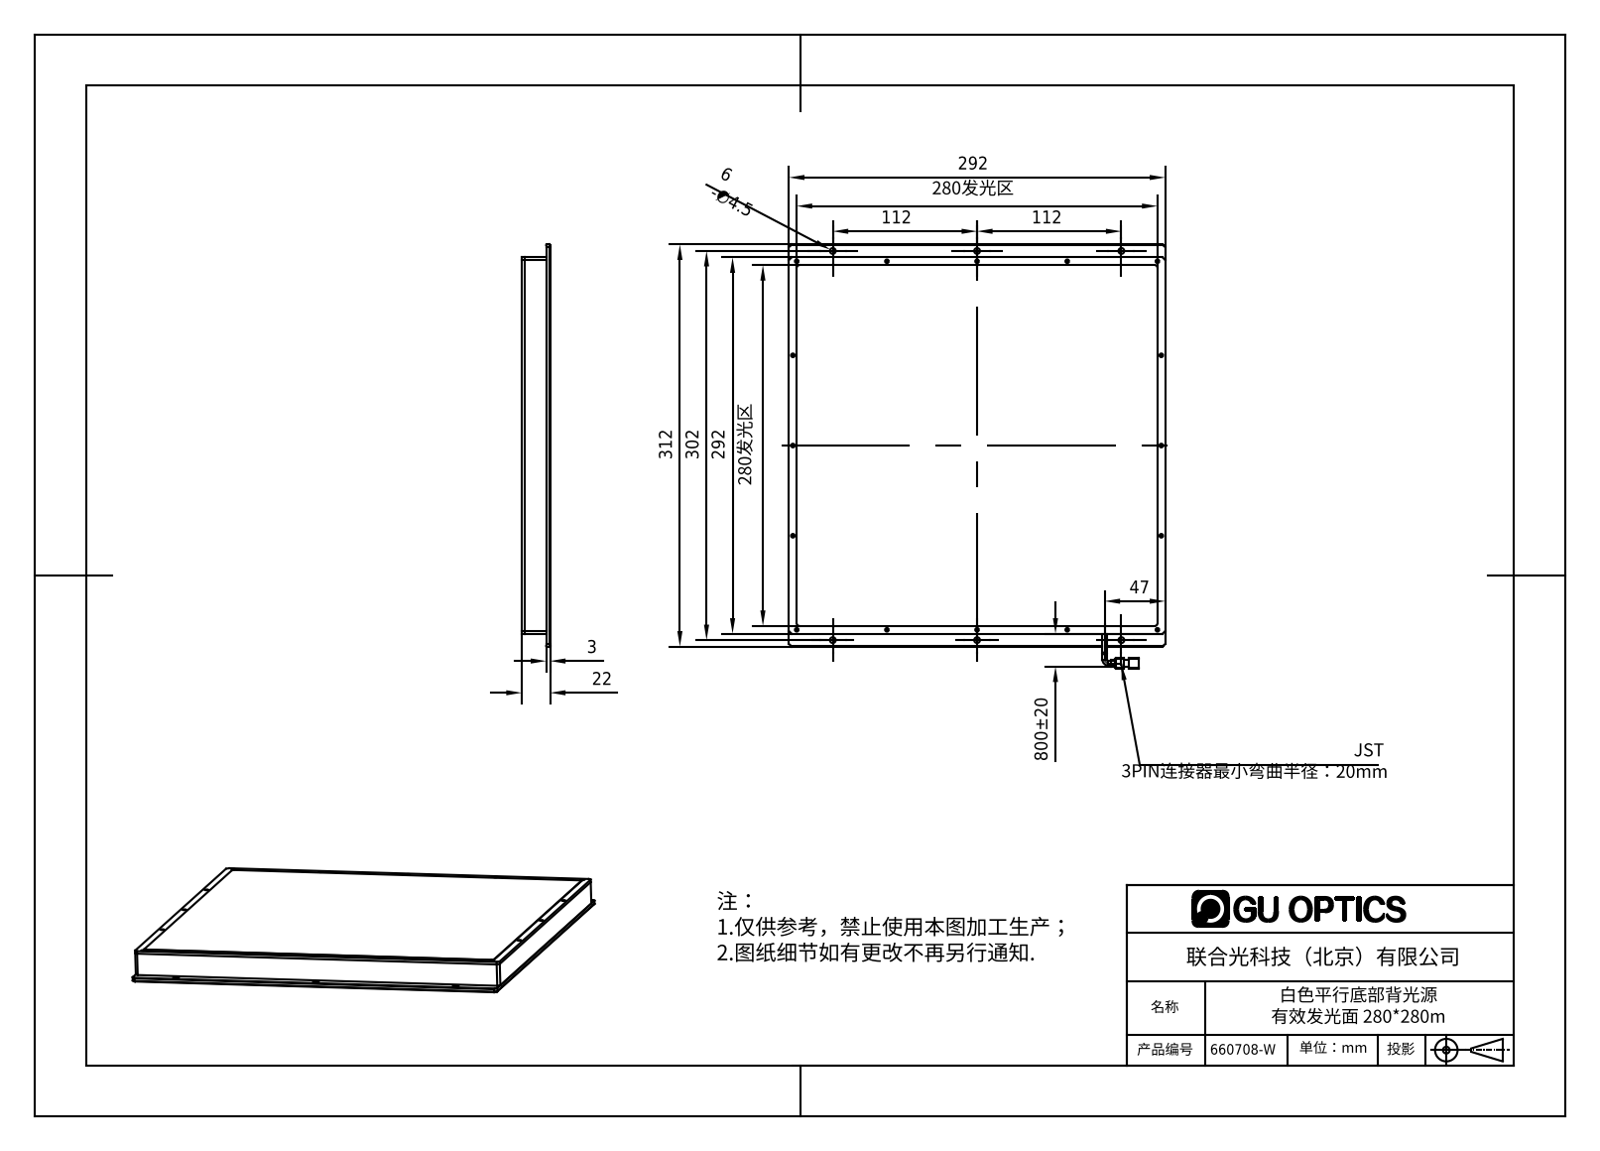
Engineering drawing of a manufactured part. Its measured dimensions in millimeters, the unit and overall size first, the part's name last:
Units: millimetres
Overall size (bounding box): 329 × 292 × 22.1
Round holes (diameter × count): ⌀1.6 ×32, ⌀1.25 ×16, ⌀1.5 ×16, ⌀2 ×16, ⌀2.4 ×16, ⌀2.8 ×16, ⌀4.5 ×6
Round bosses / shafts (diameter × count): ⌀3.5 ×2
Partial cylindrical surfaces — rounded edges, fillets, slot ends (radius × count): R0.5 ×8, R1 ×8, R2 ×6
Main face-to-face distances: 17, 3, 20, 19.1, 22.1, 2.1, 6, 286, 292, 280
Hole centre spacings: 296.98, 80, 286, 105.54, 160, 184.44, 210, 264
Volume: 564 669 mm³ · Surface area: 413 343 mm²
Bodies: 5 solids, 652 faces (220 planar, 274 cylindrical, 158 other)
Part name (STEP PRODUCT): 660708-W
STEP written by: SolidWorks 2016 (AUTOMOTIVE_DESIGN)
